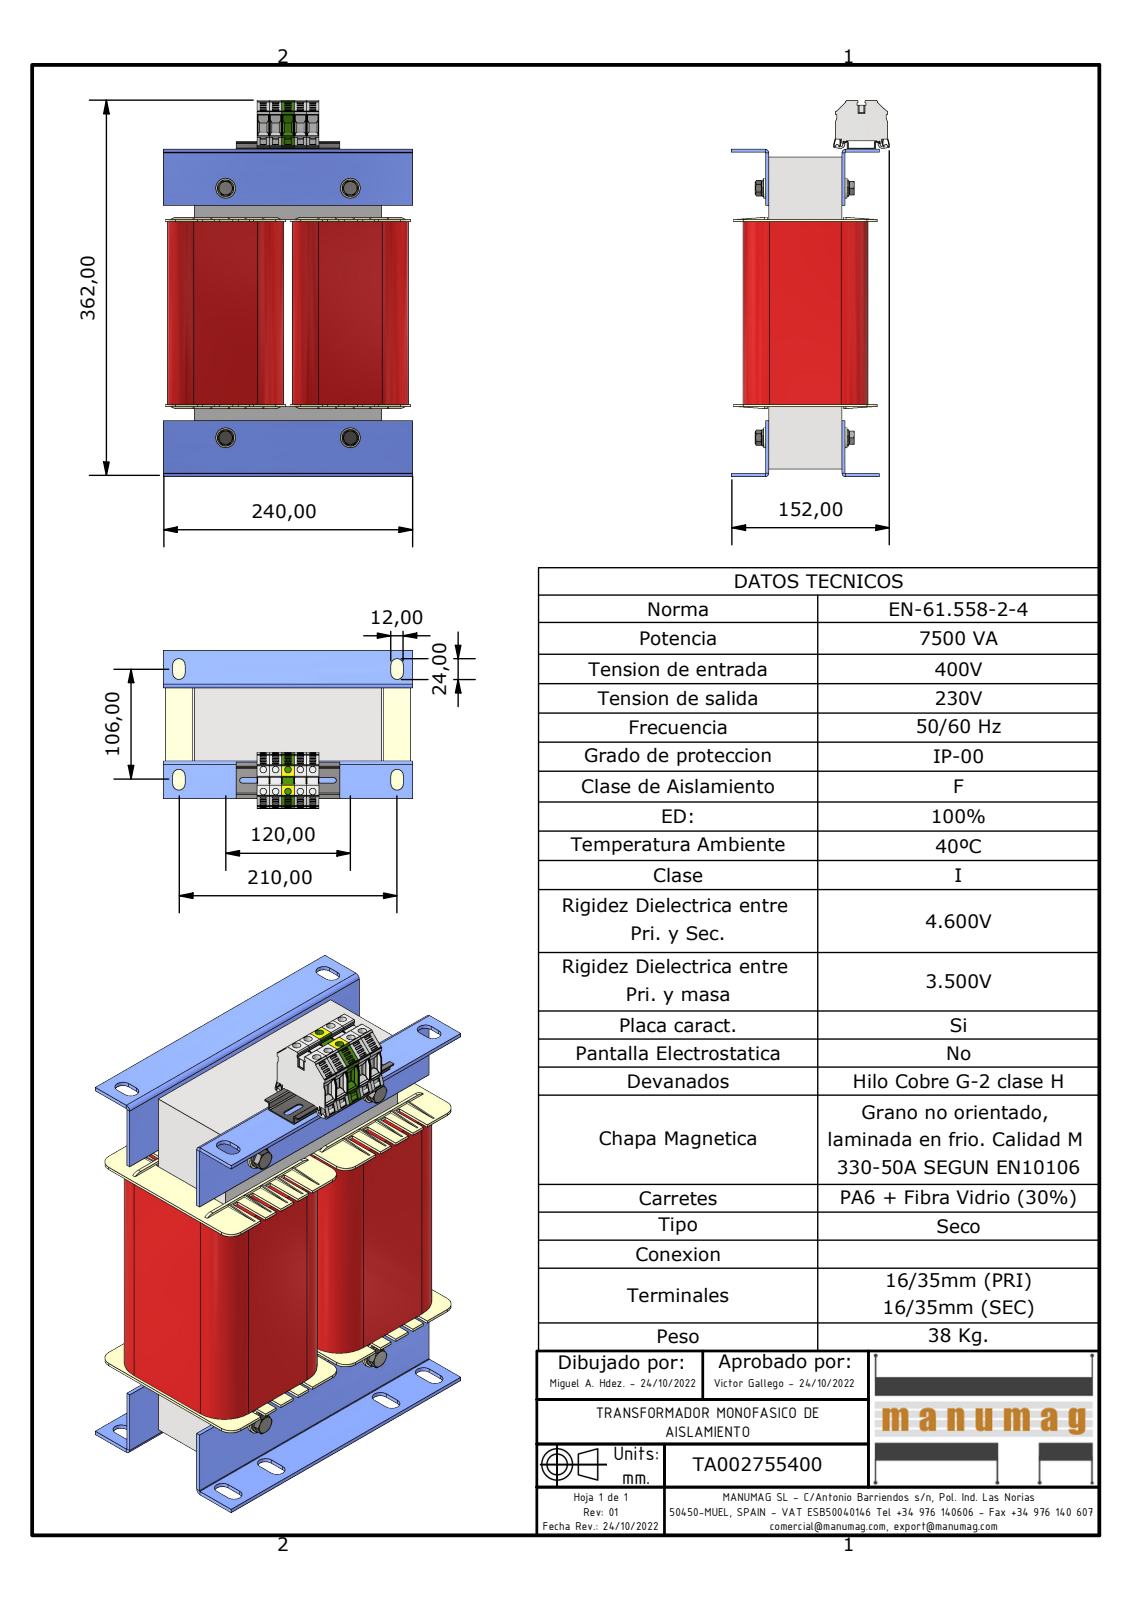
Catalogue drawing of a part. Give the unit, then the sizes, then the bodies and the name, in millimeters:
Units: millimetres
Overall size (bounding box): 362.1 × 240 × 151.8
Round holes (diameter × count): ⌀6.3 ×10, ⌀6.65 ×4, ⌀8 ×4, ⌀8.4 ×4, ⌀13 ×4
Round bosses / shafts (diameter × count): ⌀19 ×4, ⌀16 ×4, ⌀11.4 ×4, ⌀9.6 ×4, ⌀7.32 ×4
Partial cylindrical surfaces — rounded edges, fillets, slot ends (radius × count): R0.3 ×258, R1 ×24, R6 ×24, R0.25 ×16, R10 ×16, R2 ×10, R0.5 ×8, R2.6 ×8
Main face-to-face distances: 120, 1, 2.5, 22.37, 22.06, 23.37, 0.31, 1.31, 1.5, 3
Hole centre spacings: 11.9, 24.14, 23.8, 31.74, 21, 35.7, 41.42, 47.6
Volume: 6 256 000 mm³ · Surface area: 957 454 mm²
Bodies: 37 solids, 3238 faces (1956 planar, 1028 cylindrical, 254 other)
Part name (STEP PRODUCT): TA002755400; UI300 x 180 - 70 (Rc60); RC 60 UI INFERIOR; RC 60 UI SUPERIOR (+8 more)
STEP written by: Autodesk Inventor 2023 (AUTOMOTIVE_DESIGN)
